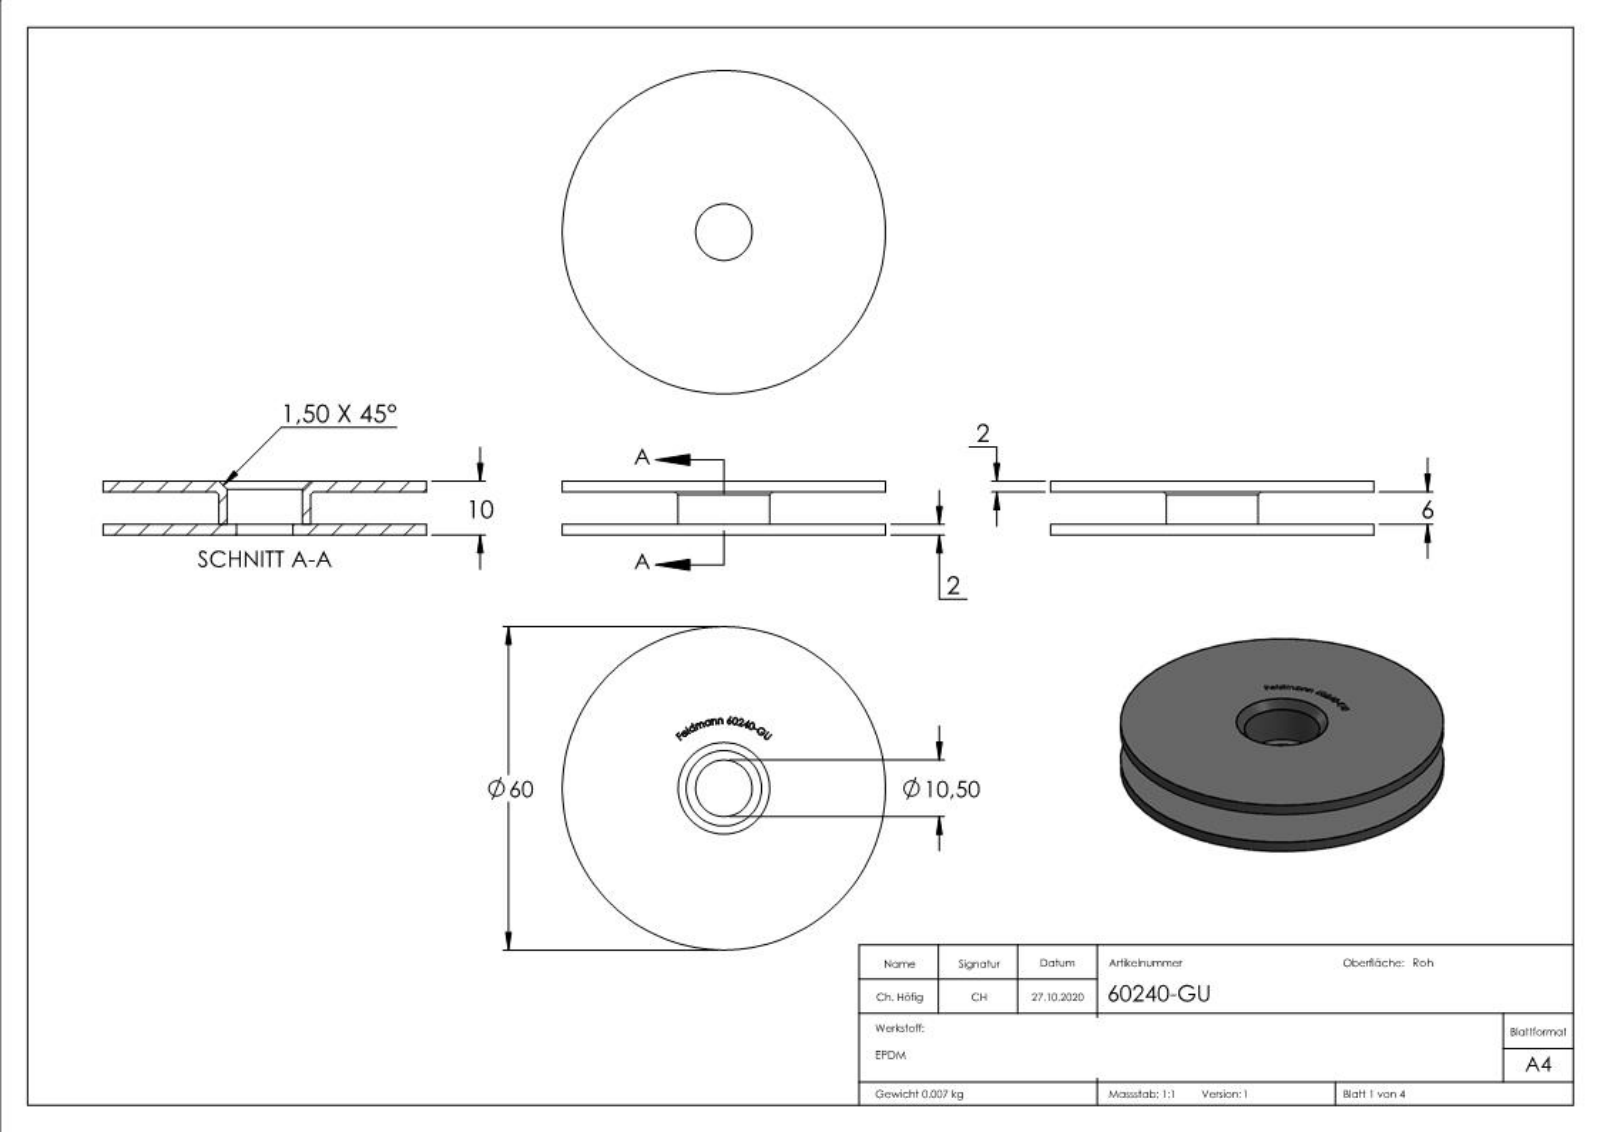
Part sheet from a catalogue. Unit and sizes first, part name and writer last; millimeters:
Units: millimetres
Overall size (bounding box): 60 × 60 × 10
Round holes (diameter × count): ⌀10.5 ×1, ⌀14 ×1
Round bosses / shafts (diameter × count): ⌀60 ×1, ⌀17 ×1
Main face-to-face distances: 2, 8, 10, 6, 9.5, 7.5, 1.5, 0.5, 0.74, 0.66
Volume: 11 218 mm³ · Surface area: 12 317 mm²
Bodies: 2 solids, 229 faces (118 planar, 10 cylindrical, 101 other)
Part name (STEP PRODUCT): 60240-GU; 60240-GU Teil2; 60240-GU Teil2_60240-GU Teil2; 60240-GU Teil1_60240-GU Teil1 (+1 more)
STEP written by: SolidWorks 2018 (CONFIG_CONTROL_DESIGN)
